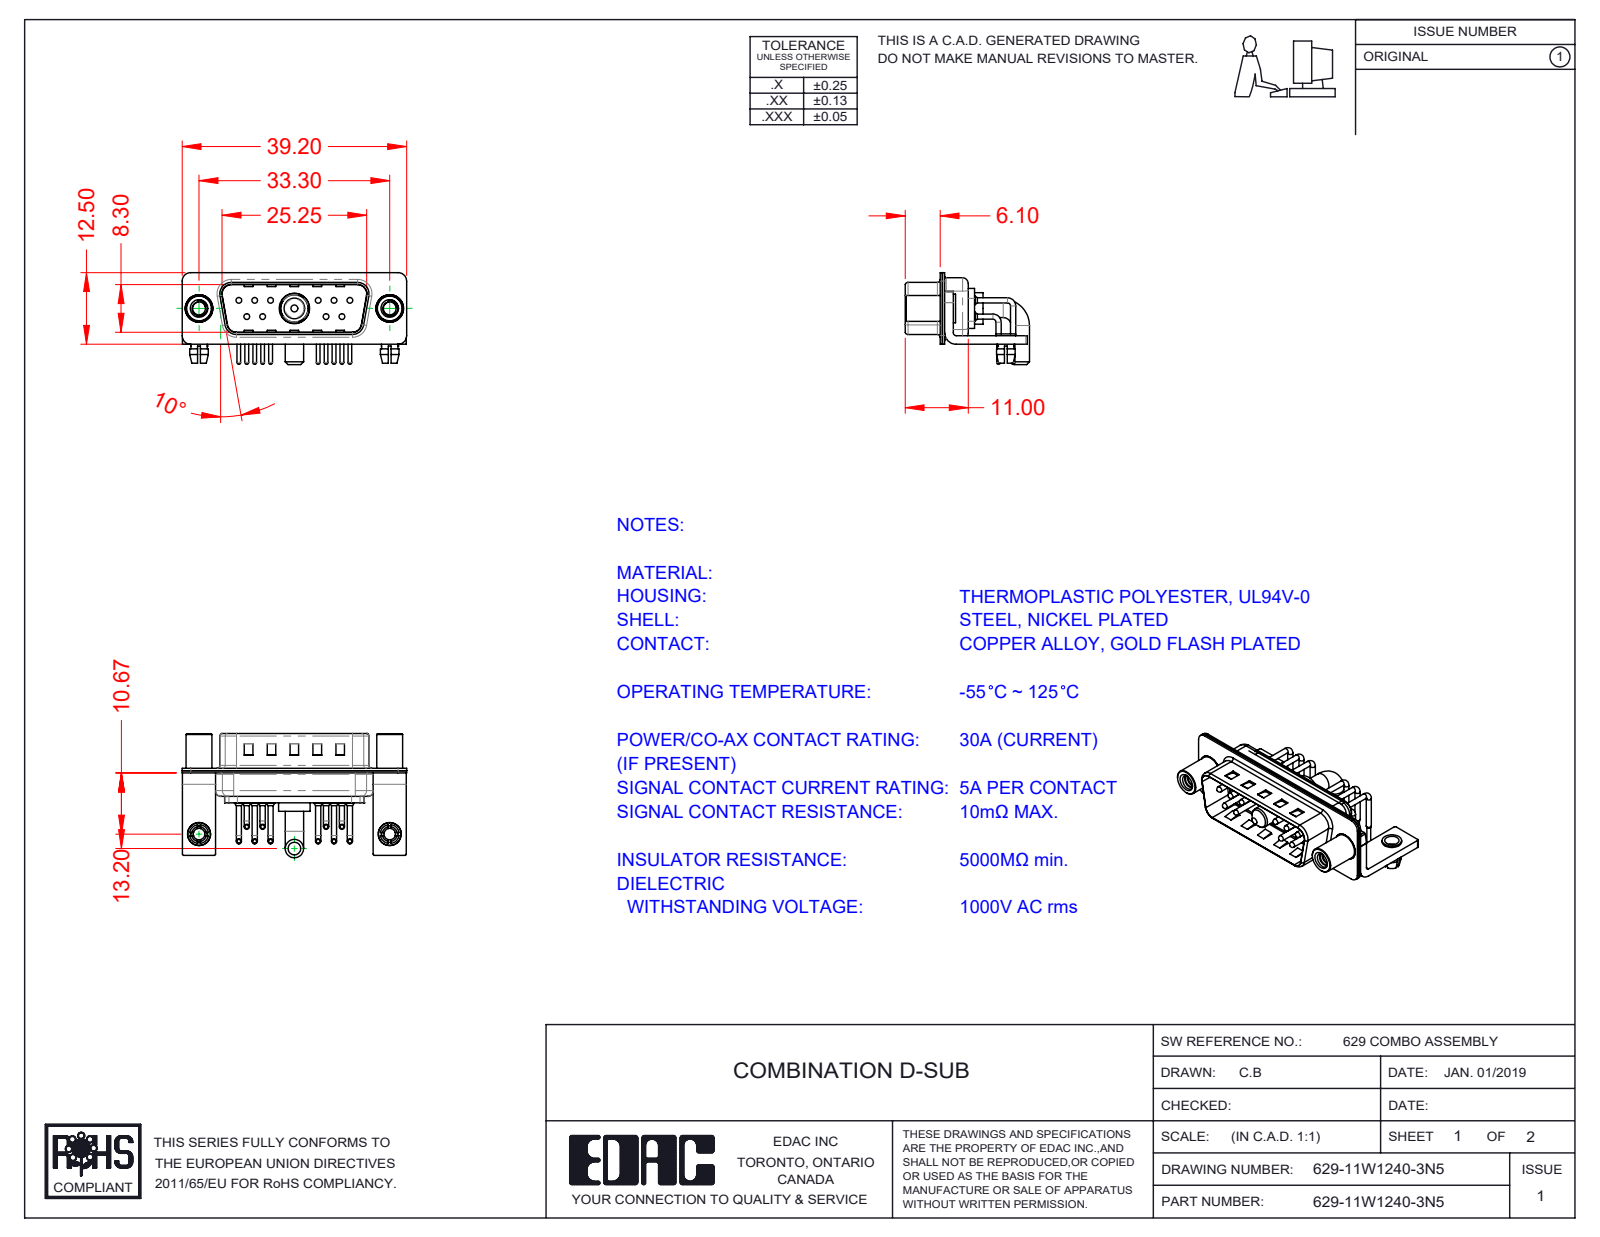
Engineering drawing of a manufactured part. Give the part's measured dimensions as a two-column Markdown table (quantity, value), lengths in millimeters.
| quantity | value |
| --- | --- |
| part name | 629Combo Shell Front_15 Contacts; Power Pin_30A RA; 629Combo Board Lock; 629-11W1240-3N5 (+6 more) |
| STEP written by | SolidWorks 2020 (CONFIG_CONTROL_DESIGN) |
| units | millimeters |
| bodies | 21 solids, 1676 faces (868 planar, 610 cylindrical, 198 other) |
| overall size | 39.2 × 21.7 × 16.05 |
| volume | 2 524 mm³ |
| surface area | 6 377 mm² |
| round holes (diameter × count) | 2 × 12, 0.75 × 10, 1.6 × 10, 2.26 × 2, 2.5 × 2, 3.2 × 2, 4 × 2, 4.8 × 2, 4.85 × 1, 5.3 × 1 |
| round bosses / shafts (diameter × count) | 0.9 × 20, 1.5 × 10, 1 × 10, 0.65 × 10, 5 × 2, 4.9 × 2, 4.5 × 2, 4 × 2 |
| partial cylindrical surfaces (radius × count) | 0.25 × 16, 1.5 × 16, 2 × 13, 1.01 × 10, 0.5 × 9, 1.6 × 8, 1 × 7, 0.6 × 4 |
| main face-to-face distances | 0.4, 0.8, 1.5, 9.5, 8.7, 9.1, 9.9, 0.6, 1.9, 5.2 |
| hole center spacings | 3.16, 2.77, 13.85, 11.08, 16.62, 5.03, 5.04, 5.54 |
